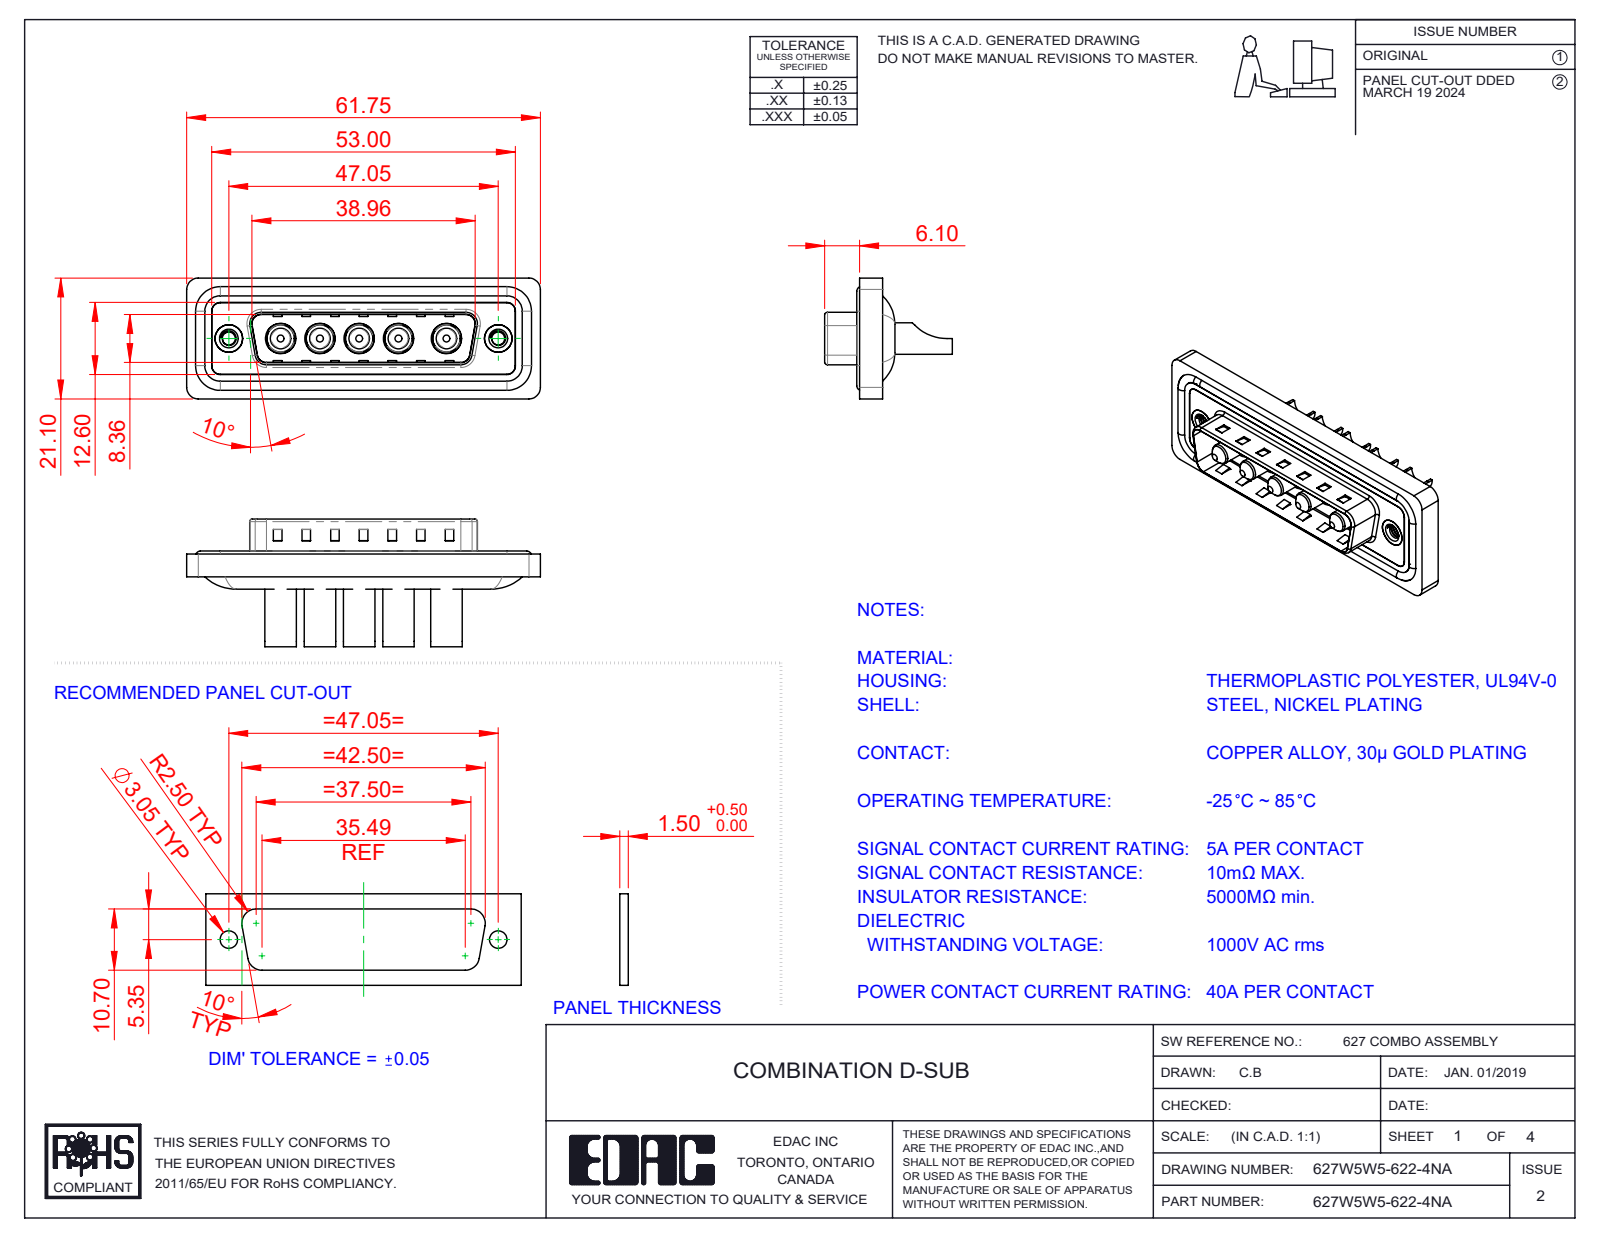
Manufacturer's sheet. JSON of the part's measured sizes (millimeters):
{"part_name": "627Combo Shell Rear_25 Contacts; 627Combo Shell Front_25 Contacts; 627W5W5-622-4NA; 627Combo Housing_5W5 (+3 more)", "step_written_by": "SolidWorks 2023 (CONFIG_CONTROL_DESIGN)", "units": "millimeters", "bodies": {"solids": 17, "faces": 696, "planar": 269, "cylindrical": 290, "other": 137}, "overall_size": [61.75, 22.3, 21.1], "volume_mm3": 7674, "surface_area_mm2": 12493, "round_holes": [[4.6, 5], [4.85, 5], [5.3, 5], [2.26, 2], [4, 2], [4.8, 2], [5, 2]], "round_bosses_or_shafts": [[5.5, 5], [5.2, 5], [4.75, 5], [3.75, 5], [3.6, 5], [1.6, 4], [4.9, 2]], "partial_cylinders_radius": [[1.5, 22], [2, 18], [0.5, 8], [1.6, 8], [2.1, 5], [0.25, 4], [0.6, 4], [0.65, 4]], "face_to_face_distances": [0.4, 0.5, 1.1, 1.5, 3.1, 1.6, 2.9, 0.82, 9.58, 5.65], "hole_center_spacings": [6.86, 9.04, 13.73, 38.01, 6.87, 8.37, 8.38, 9.05]}
